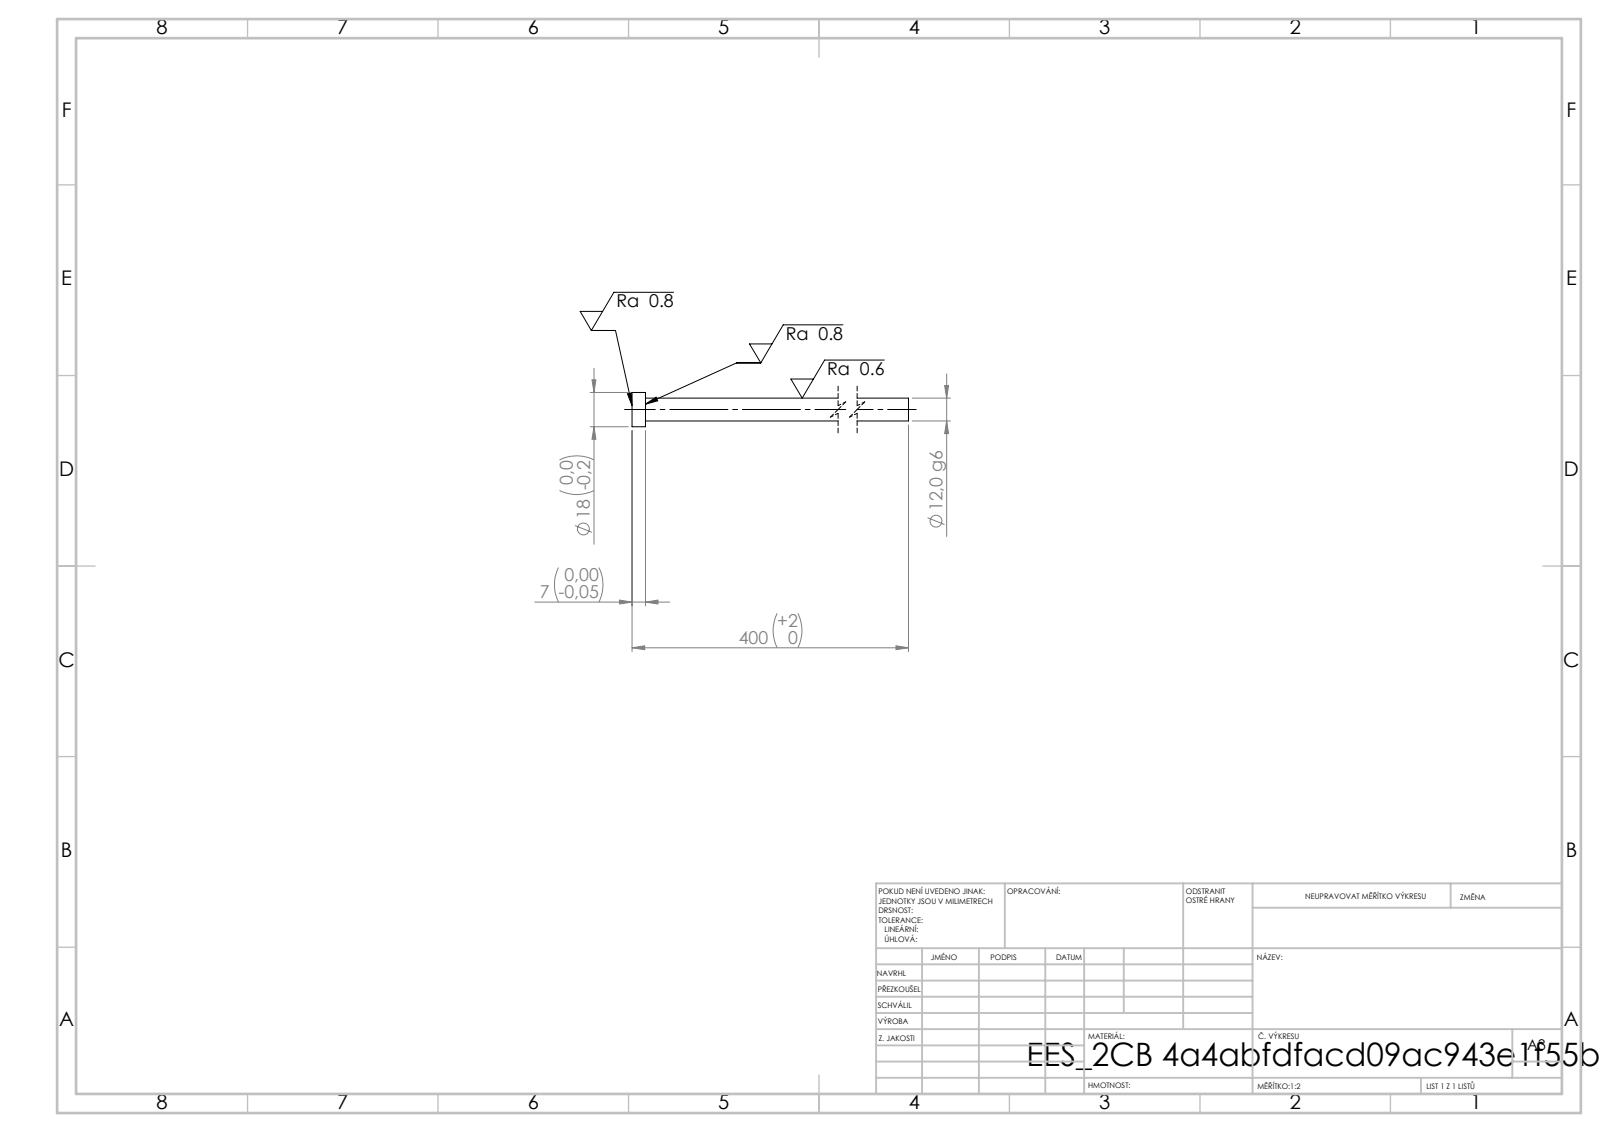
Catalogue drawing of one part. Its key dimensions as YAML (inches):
step_written_by: "SolidWorks 2019 (CONFIG_CONTROL_DESIGN)"
units: inches
bodies: {solids: 1, faces: 7, planar: 3, cylindrical: 4, other: 0}
overall_size: [15.748, 0.709, 0.709]
volume: 2.821
surface_area: 24.37
round_bosses_or_shafts:
  - {diameter: 0.709, count: 1}
  - {diameter: 0.472, count: 1}
face_to_face_distances: [0.276, 15.748, 15.472]
